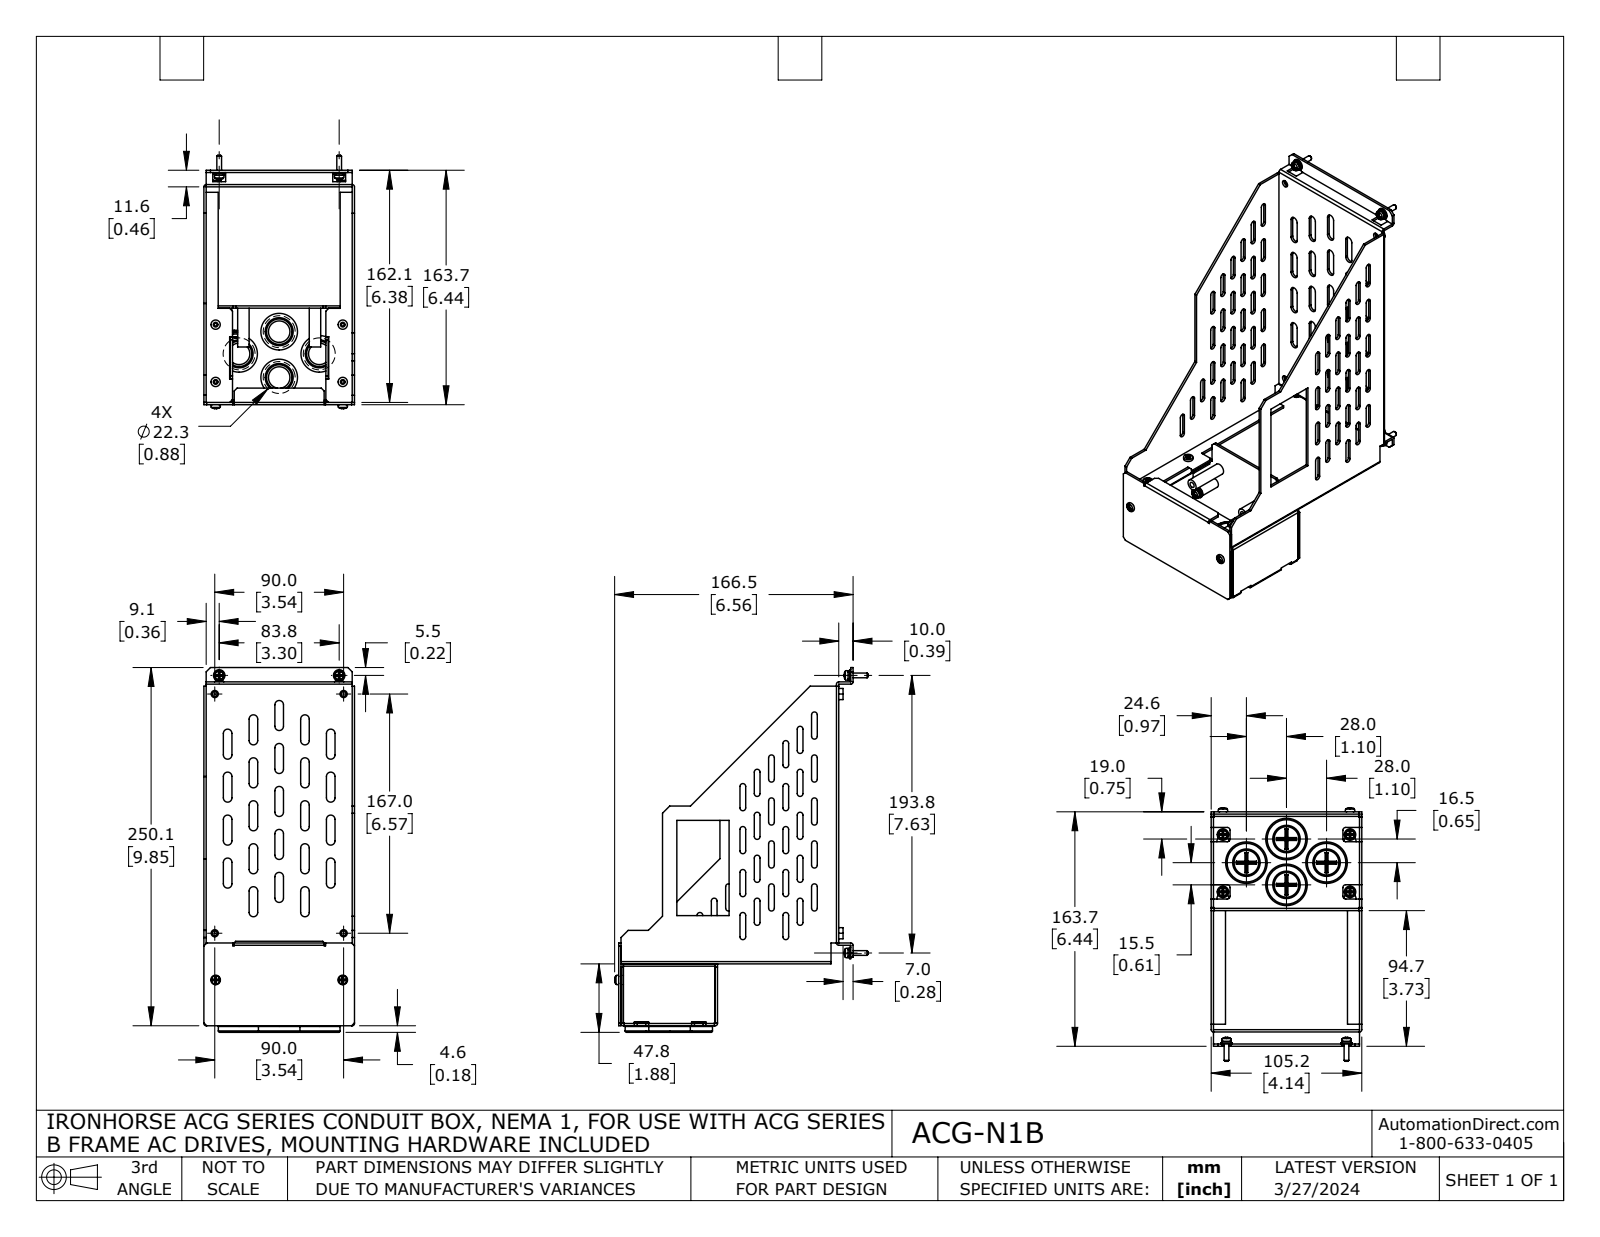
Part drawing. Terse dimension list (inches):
name: ACG-N1B
written by: SolidWorks 2021 (AUTOMOTIVE_DESIGN)
unit: in
bodies: 18 solids, 1343 faces (698 planar, 506 cylindrical, 139 other)
size: 10.028 × 6.97 × 4.142
volume: 8.945 in³; area: 294.6 in²
holes: 10× ⌀0.13, 4× ⌀0.197, 4× ⌀0.335, 4× ⌀0.677, 4× ⌀0.878, 4× ⌀1.024, 3× ⌀0.157, 2× ⌀0.169
bosses: 11× ⌀0.315, 9× ⌀0.259, 6× ⌀0.256, 5× ⌀0.13, 4× ⌀1.142, 4× ⌀1.008, 4× ⌀0.85, 1× ⌀0.276
rounds: 68× R0.079, 46× R0.118, 24× R0.02, 17× R0.063, 4× R0.089, 4× R0.098, 3× R0.197
face distances: 0.063, 4.079, 4.142, 4.016, 5.988, 2.654, 3.335, 5.925, 1.701, 2.591
hole spacings: 3.496, 0.197, 1.575, 3.502, 3.834, 1.26, 0.826, 0.865
